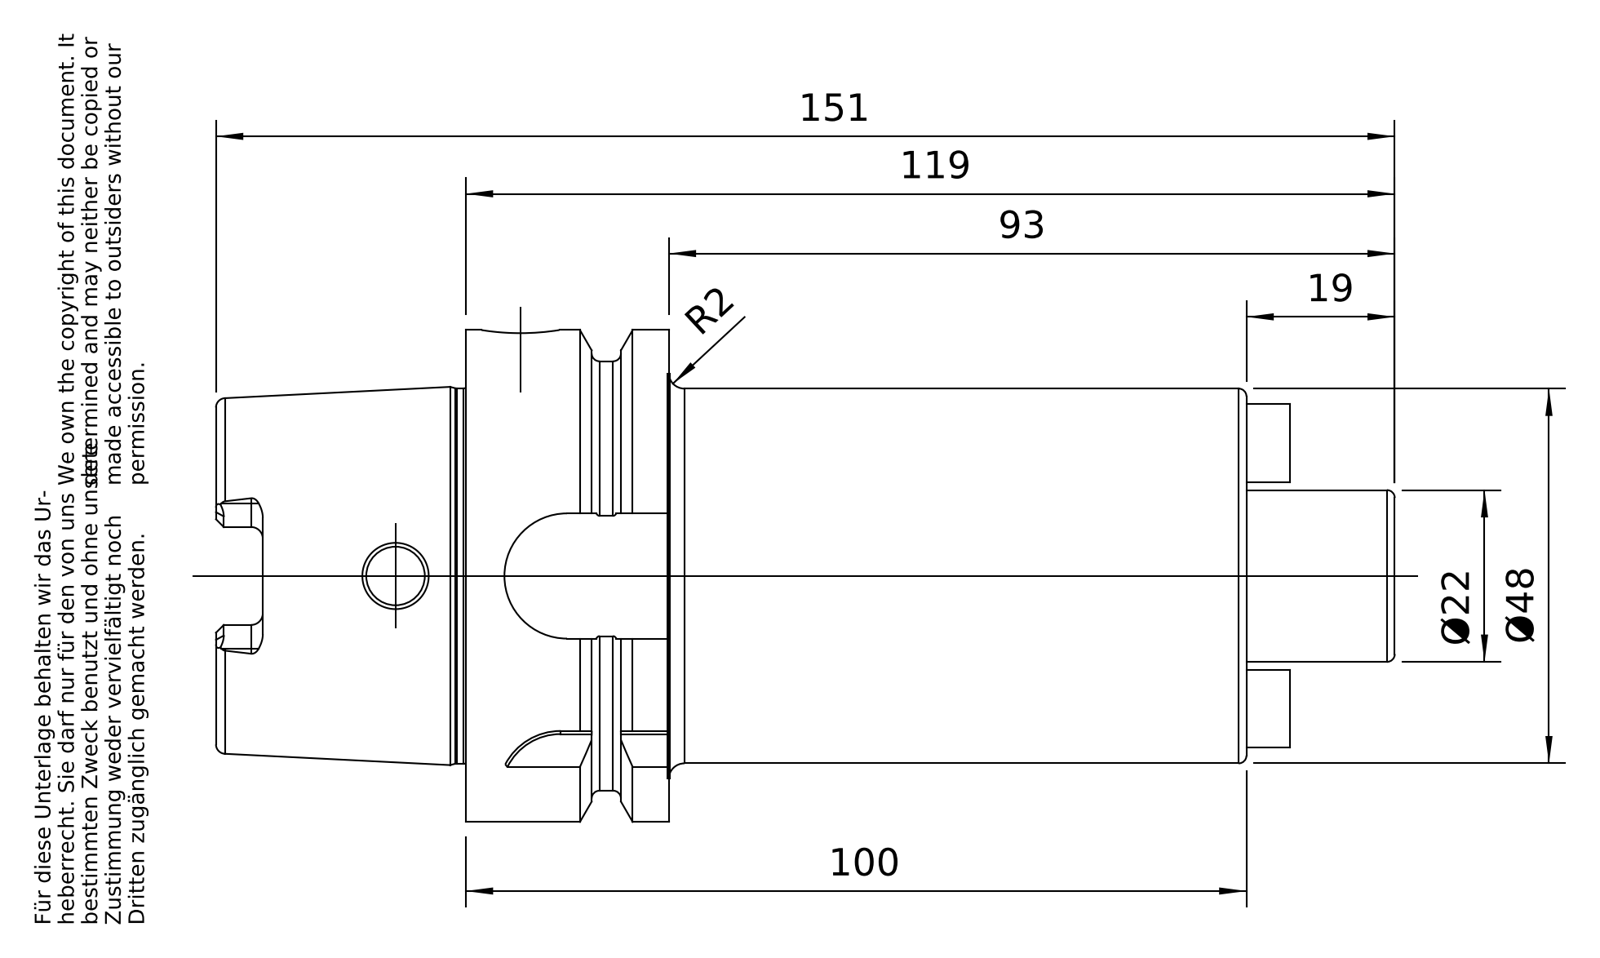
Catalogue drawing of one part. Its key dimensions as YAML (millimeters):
part_name: "A63-051-22"
step_written_by: "PRO/ENGINEER BY PARAMETRIC TECHNOLOGY CORPORATION, 2010430 (CONFIG_CONTROL_DESIGN)"
units: millimeters
bodies: {solids: 1, faces: 190, planar: 68, cylindrical: 52, other: 70}
overall_size: [151, 63, 63]
volume: 222197
surface_area: 36857
round_holes:
  - {diameter: 10, count: 2}
  - {diameter: 7.5, count: 1}
  - {diameter: 8.5, count: 1}
  - {diameter: 16.92, count: 1}
  - {diameter: 18.32, count: 1}
  - {diameter: 18.66, count: 1}
  - {diameter: 34, count: 1}
  - {diameter: 40, count: 1}
round_bosses_or_shafts:
  - {diameter: 63, count: 1}
  - {diameter: 55, count: 1}
  - {diameter: 48.04, count: 1}
  - {diameter: 48, count: 1}
  - {diameter: 22, count: 1}
  - {diameter: 18, count: 1}
partial_cylinders:
  - {radius: 1.5, count: 6}
  - {radius: 3, count: 4}
  - {radius: 8, count: 1}
  - {radius: 8.02, count: 1}
  - {radius: 9.02, count: 1}
face_to_face_distances: [100, 26, 74, 10, 16, 90, 32, 42, 58, 132]
